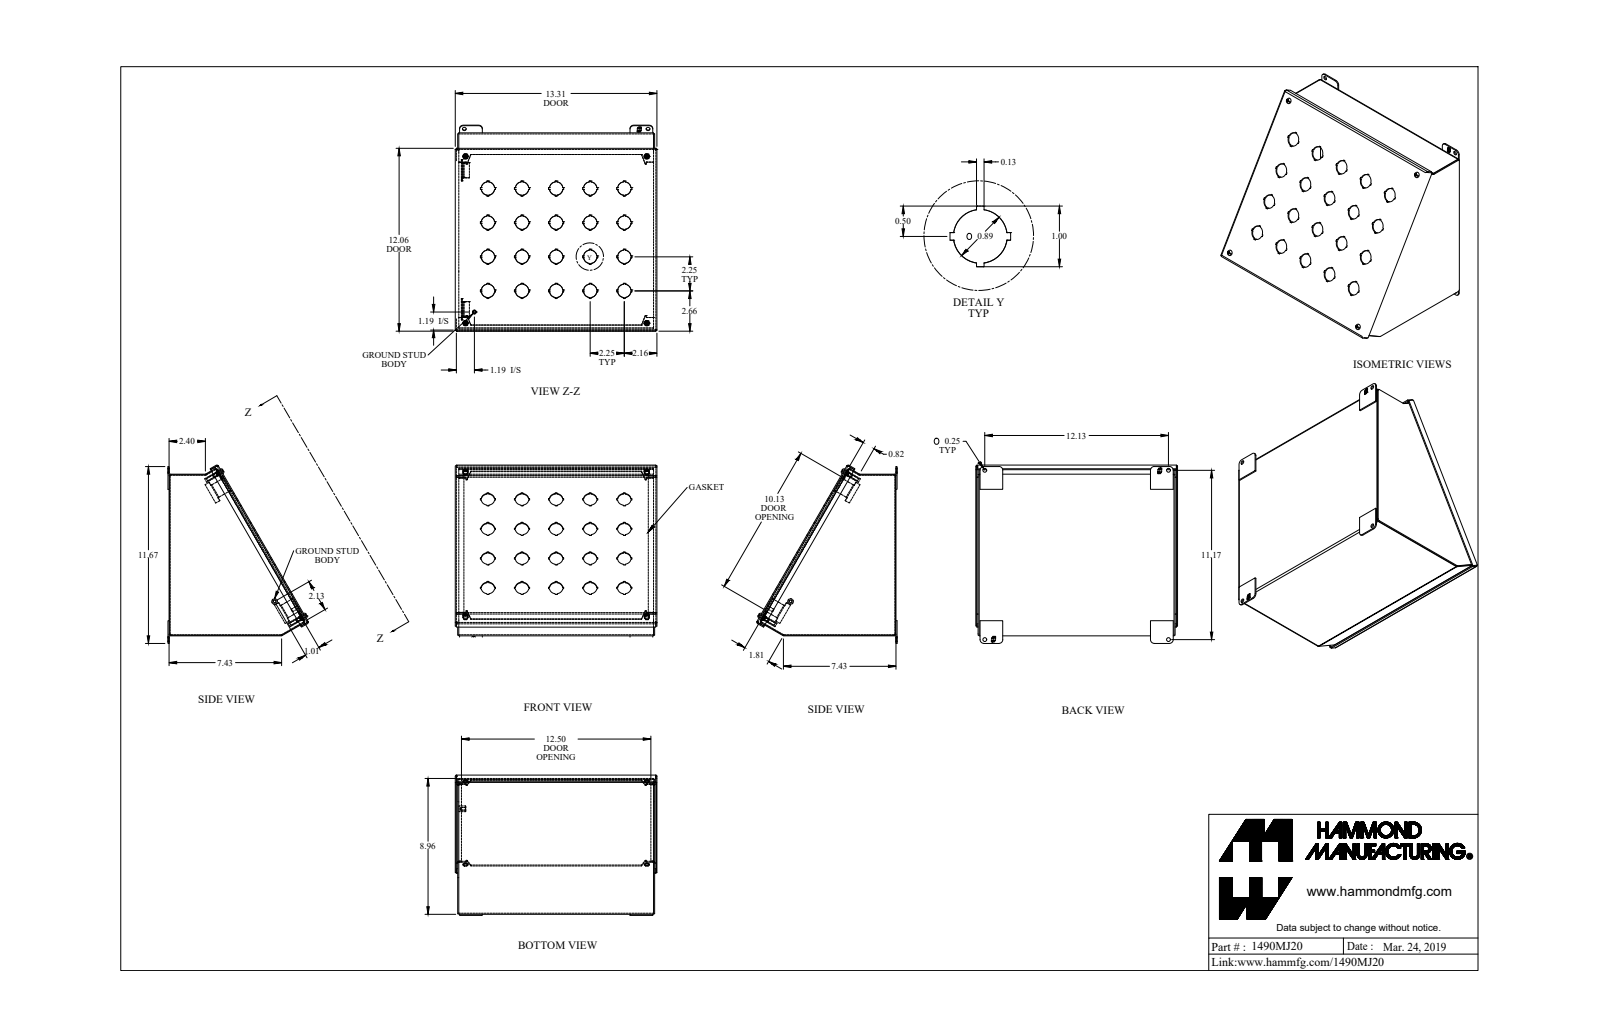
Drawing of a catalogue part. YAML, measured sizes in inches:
part_name: "1490MJ20_Default"
step_written_by: "SolidWorks 2019 (CONFIG_CONTROL_DESIGN)"
units: inches
bodies: {solids: 26, faces: 1013, planar: 723, cylindrical: 252, other: 38}
overall_size: [13.312, 11.788, 9.303]
volume: 44.93
surface_area: 1275
round_holes:
  - {diameter: 0.875, count: 10}
  - {diameter: 0.875, count: 10}
  - {diameter: 0.25, count: 8}
  - {diameter: 0.159, count: 4}
  - {diameter: 0.12, count: 1}
  - {diameter: 0.136, count: 1}
  - {diameter: 0.156, count: 1}
round_bosses_or_shafts:
  - {diameter: 0.39, count: 4}
  - {diameter: 0.275, count: 4}
  - {diameter: 0.19, count: 4}
  - {diameter: 0.148, count: 4}
  - {diameter: 0.375, count: 1}
  - {diameter: 0.29, count: 1}
partial_cylinders:
  - {radius: 0.108, count: 18}
  - {radius: 0.036, count: 12}
  - {radius: 0.029, count: 9}
  - {radius: 0.086, count: 9}
  - {radius: 0.25, count: 8}
  - {radius: 0.125, count: 4}
  - {radius: 0.16, count: 4}
  - {radius: 0.171, count: 4}
face_to_face_distances: [0.072, 12.928, 12.856, 13, 10.595, 10.667, 10.523, 11.678, 0.222, 0.156]
hole_center_spacings: [5.031, 2.25, 3.182, 7.115, 4.5, 6.364, 8.112, 6.75]
